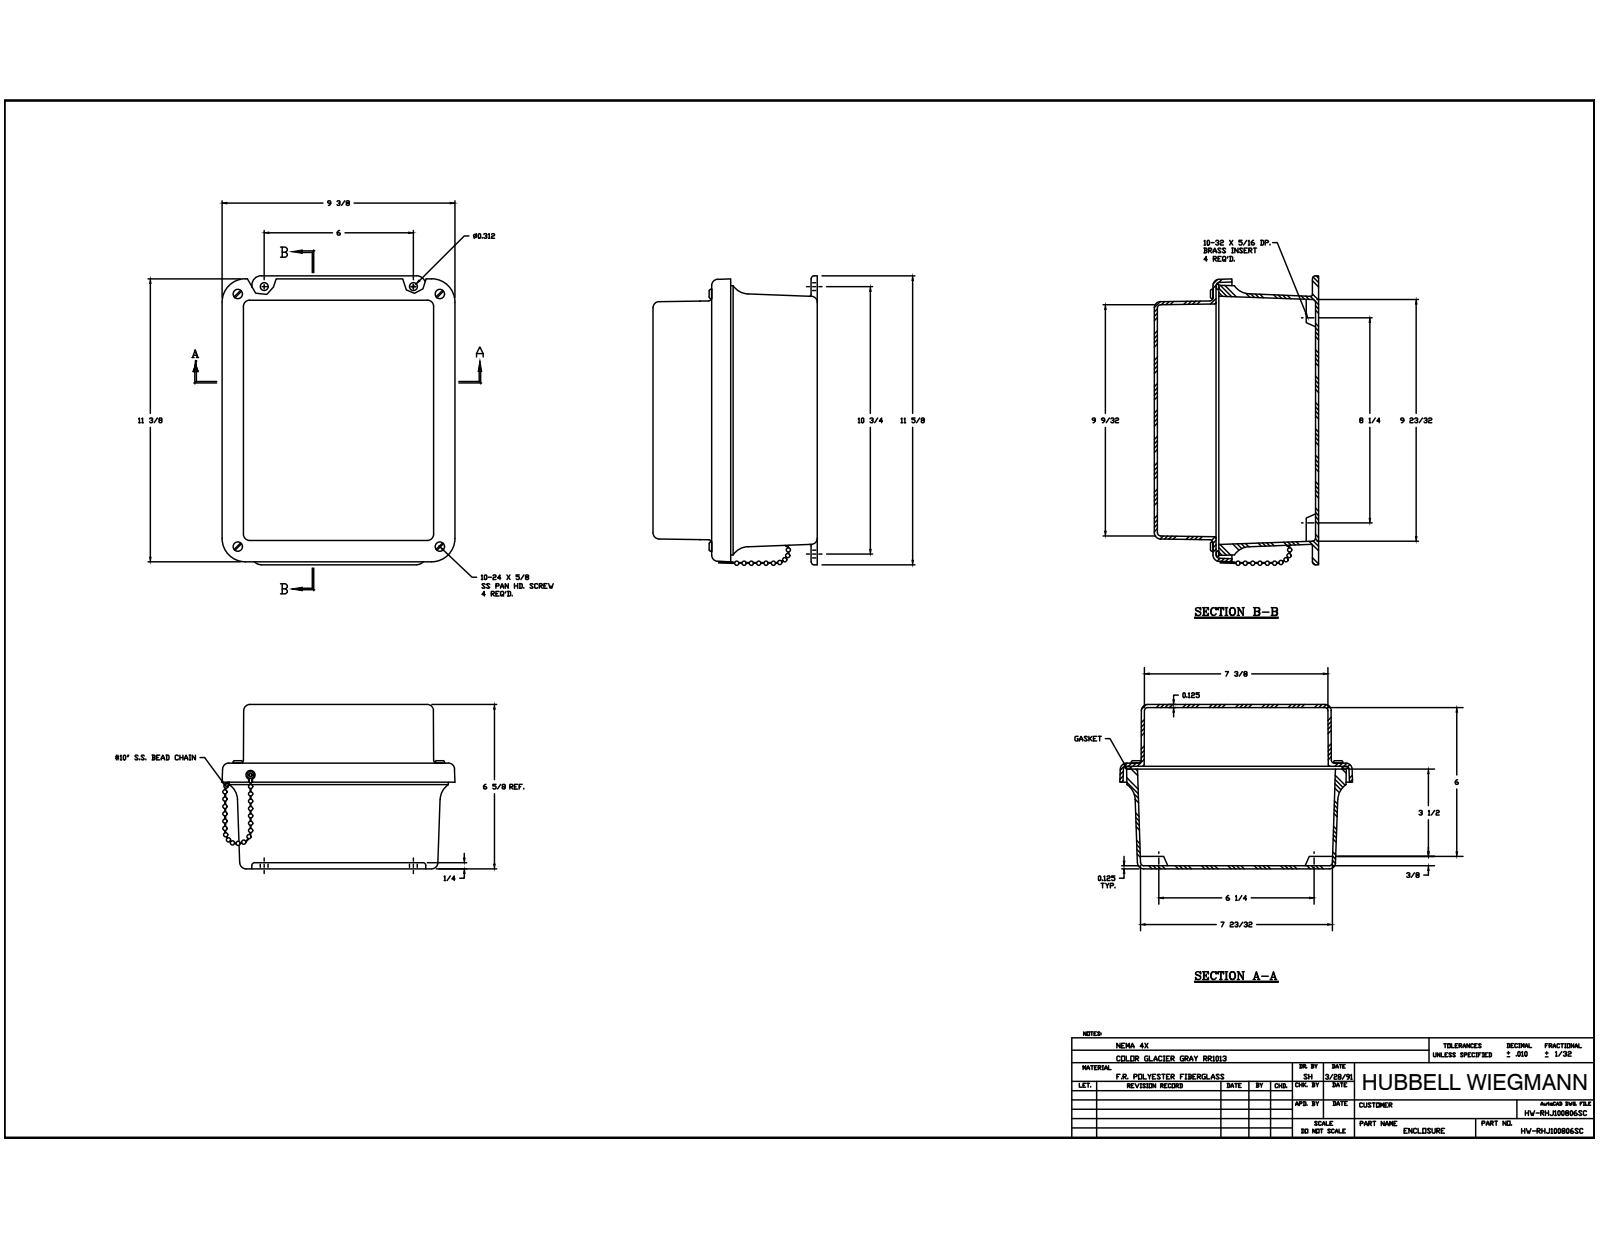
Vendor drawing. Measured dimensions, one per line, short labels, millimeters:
name: J1008W_5; RMINS45821P_139; RMINS45821P_140; RMINS45821P_141 (+8 more)
written by: Autodesk Inventor 2014 (AUTOMOTIVE_DESIGN)
unit: mm
bodies: 21 solids, 896 faces (197 planar, 295 cylindrical, 404 other)
size: 308.19 × 246.31 × 167.11
volume: 1 116 000 mm³; area: 601 348 mm²
holes: 5× ⌀3.56, 5× ⌀3.86, 4× ⌀3.68, 4× ⌀3.96, 4× ⌀5.54, 2× ⌀4.76, 1× ⌀3.2
bosses: 8× ⌀6.86, 4× ⌀4.83, 4× ⌀3.97, 2× ⌀9.52, 2× ⌀6.35, 2× ⌀3.17, 1× ⌀7.19
rounds: 24× R3.17, 20× R0.79, 12× R6.35, 4× R5.08, 4× R9.53, 4× R19.05, 2× R0.25, 2× R1.6
face distances: 3.17, 3.18, 160.76, 163.93, 167.11, 163.94, 103.99, 100.82, 59.94, 63.12
hole spacings: 33.96, 184.17, 234.96, 296.6, 63.5, 152.4, 158.76, 206.38
